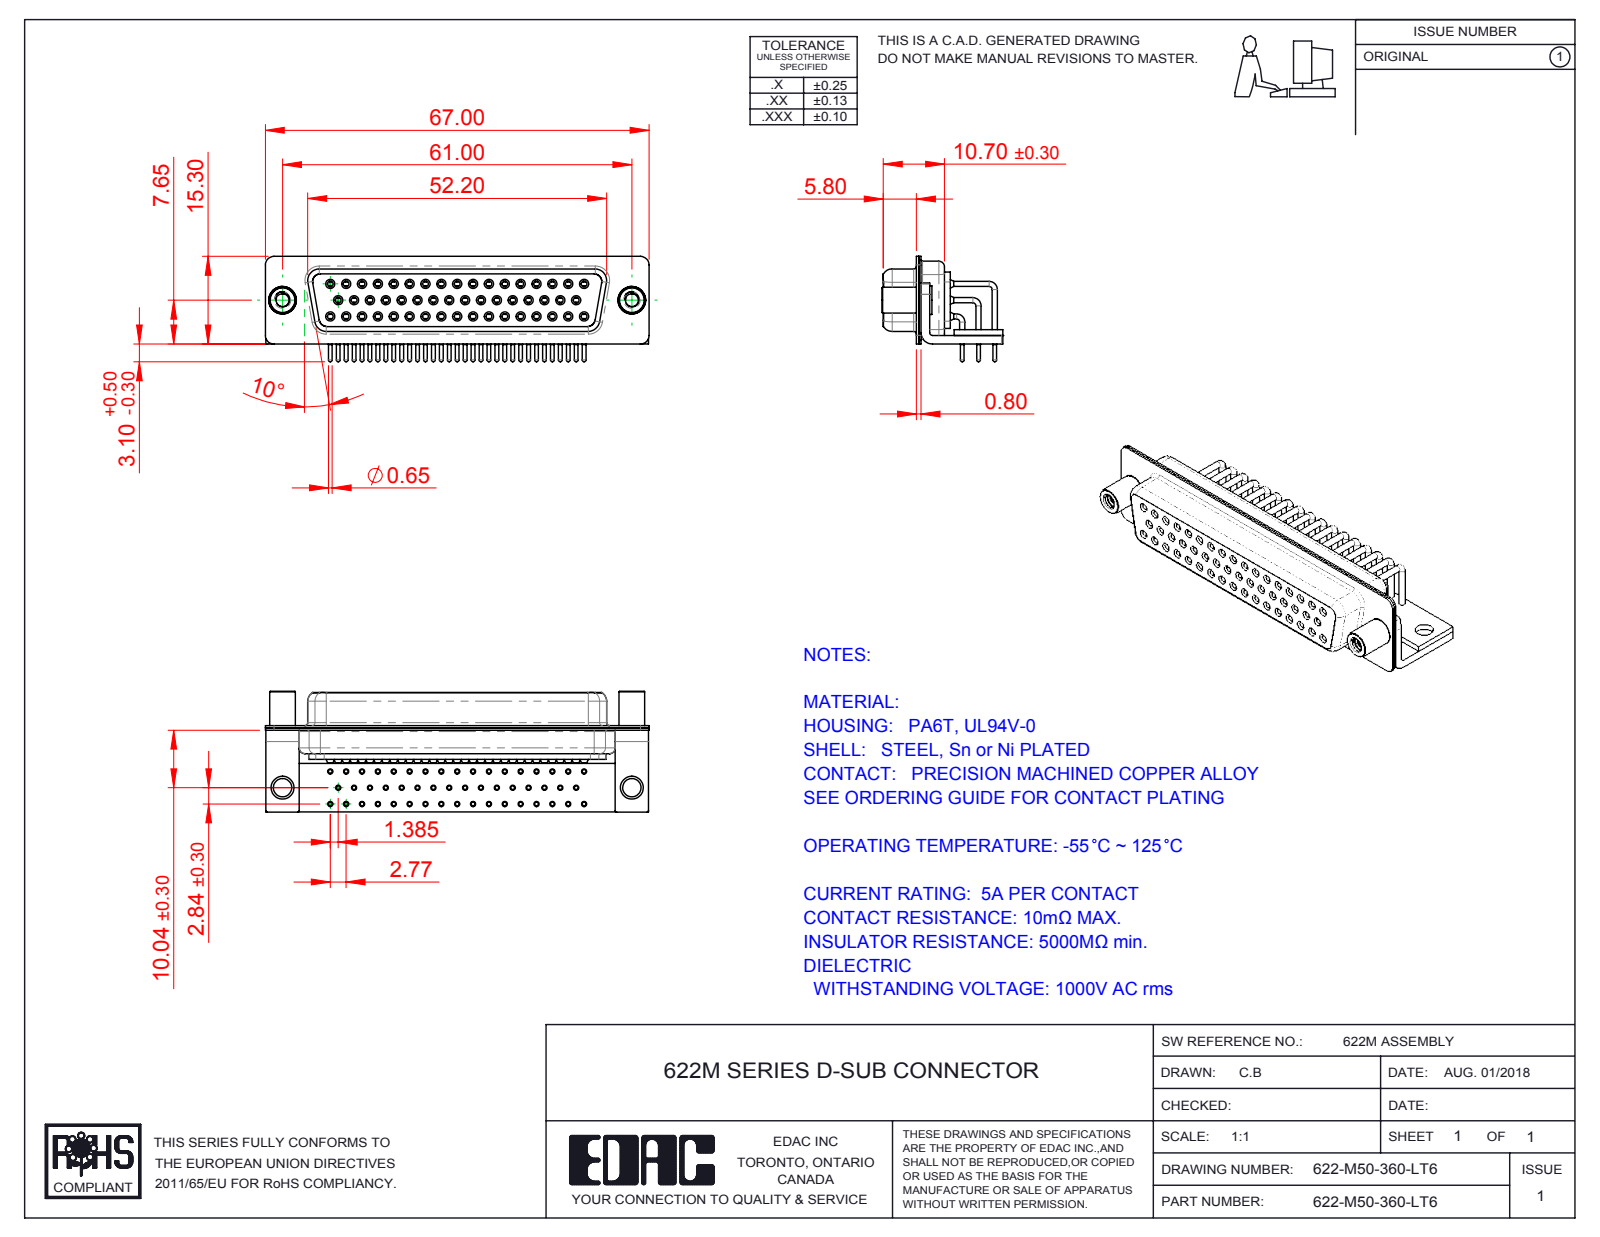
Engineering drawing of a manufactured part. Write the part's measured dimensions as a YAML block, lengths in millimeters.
part_name: "622M Shell Rear_50 Contacts; 622M Shell Front_50 Contacts; 622M Housing_50 Contacts; 622-M50-360-LT6 (+6 more)"
step_written_by: "SolidWorks 2016 (CONFIG_CONTROL_DESIGN)"
units: millimeters
bodies: {solids: 58, faces: 3129, planar: 845, cylindrical: 1451, other: 833}
overall_size: [67, 21.1, 18.4]
volume: 7871
surface_area: 18434
round_holes:
  - {diameter: 0.9, count: 50}
  - {diameter: 1, count: 50}
  - {diameter: 1.1, count: 50}
  - {diameter: 1.7, count: 50}
  - {diameter: 1.8, count: 50}
  - {diameter: 2, count: 50}
  - {diameter: 2.26, count: 2}
  - {diameter: 3.2, count: 2}
  - {diameter: 4, count: 2}
  - {diameter: 4.8, count: 2}
round_bosses_or_shafts:
  - {diameter: 0.9, count: 59}
  - {diameter: 1.6, count: 50}
  - {diameter: 1.5, count: 50}
  - {diameter: 0.65, count: 50}
  - {diameter: 5, count: 2}
  - {diameter: 4.9, count: 2}
  - {diameter: 4.5, count: 2}
partial_cylinders:
  - {radius: 0.25, count: 16}
  - {radius: 1.5, count: 16}
  - {radius: 2, count: 13}
  - {radius: 1.35, count: 8}
  - {radius: 1.6, count: 8}
  - {radius: 0.5, count: 5}
  - {radius: 0.6, count: 4}
  - {radius: 0.65, count: 4}
face_to_face_distances: [0.4, 1, 2.2, 0.85, 1.35, 11.85, 12.25, 5.8, 0.8, 5.9]
hole_center_spacings: [2.77, 3.16, 5.54, 8.31, 11.08, 13.85, 16.62, 19.39]
